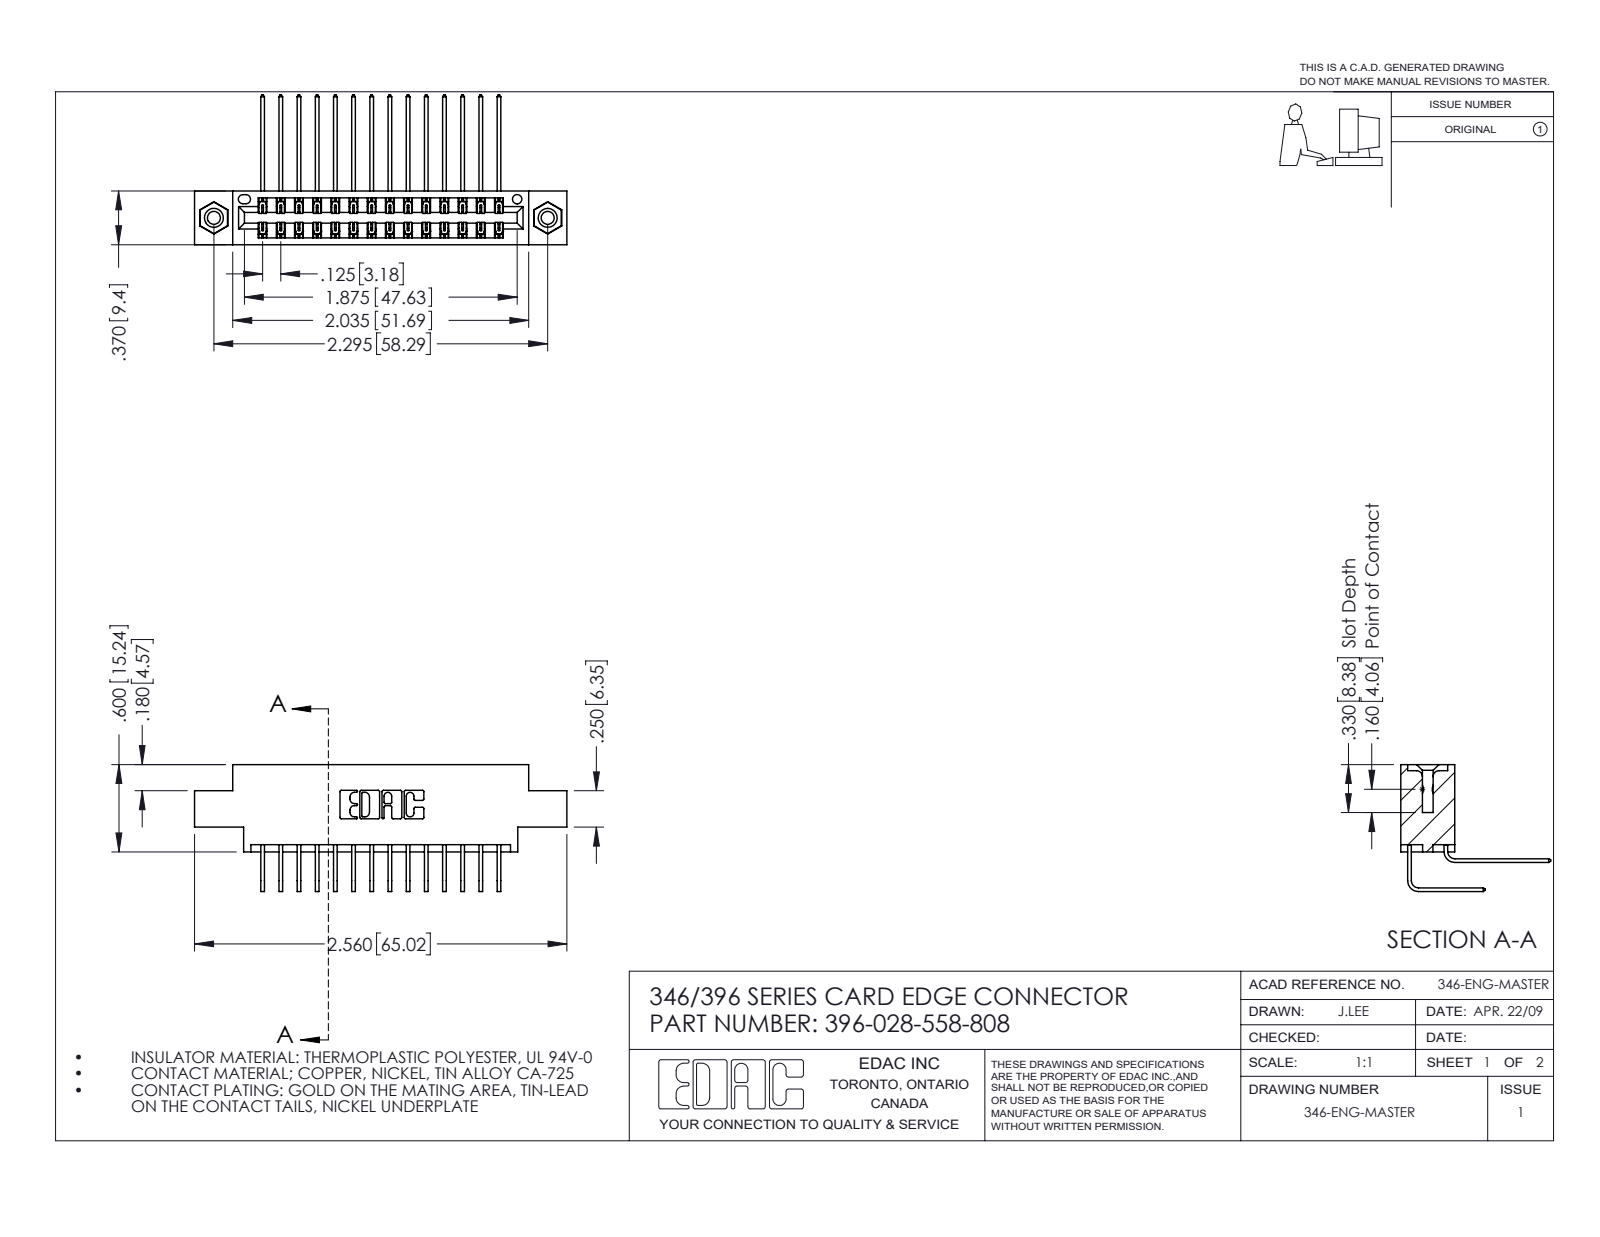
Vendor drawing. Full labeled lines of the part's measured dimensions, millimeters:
Part name (STEP PRODUCT): 345-292-001_558 Tail - 2; 345-292-001_558 559 Tail - 1; 346 Part_0.170 Offset - 0.156 Dia-TI; 345-250-001_345-250-003-102 (+1 more)
STEP written by: SolidWorks 2016 (CONFIG_CONTROL_DESIGN)
Units: millimetres
Bodies: 31 solids, 1698 faces (1148 planar, 534 cylindrical, 16 other)
Overall size (bounding box): 65 × 26.2 × 22.2
Volume: 6 130 mm³ · Surface area: 8 955 mm²
Round holes (diameter × count): ⌀2.3 ×2, ⌀3.2 ×2, ⌀4 ×2, ⌀1.6 ×1
Round bosses / shafts (diameter × count): ⌀3.9 ×2
Partial cylindrical surfaces — rounded edges, fillets, slot ends (radius × count): R0.2 ×42, R0.3 ×22, R0.2 ×6, R0.8 ×6, R0.7 ×3, R0.4 ×2, R0.6 ×2, R0.6 ×2
Main face-to-face distances: 1.2, 8.2, 9.4, 6.4, 0.6, 1.8, 7.6, 5.6, 7, 3.8
Hole centre spacings: 6.2, 53.1, 58.3
